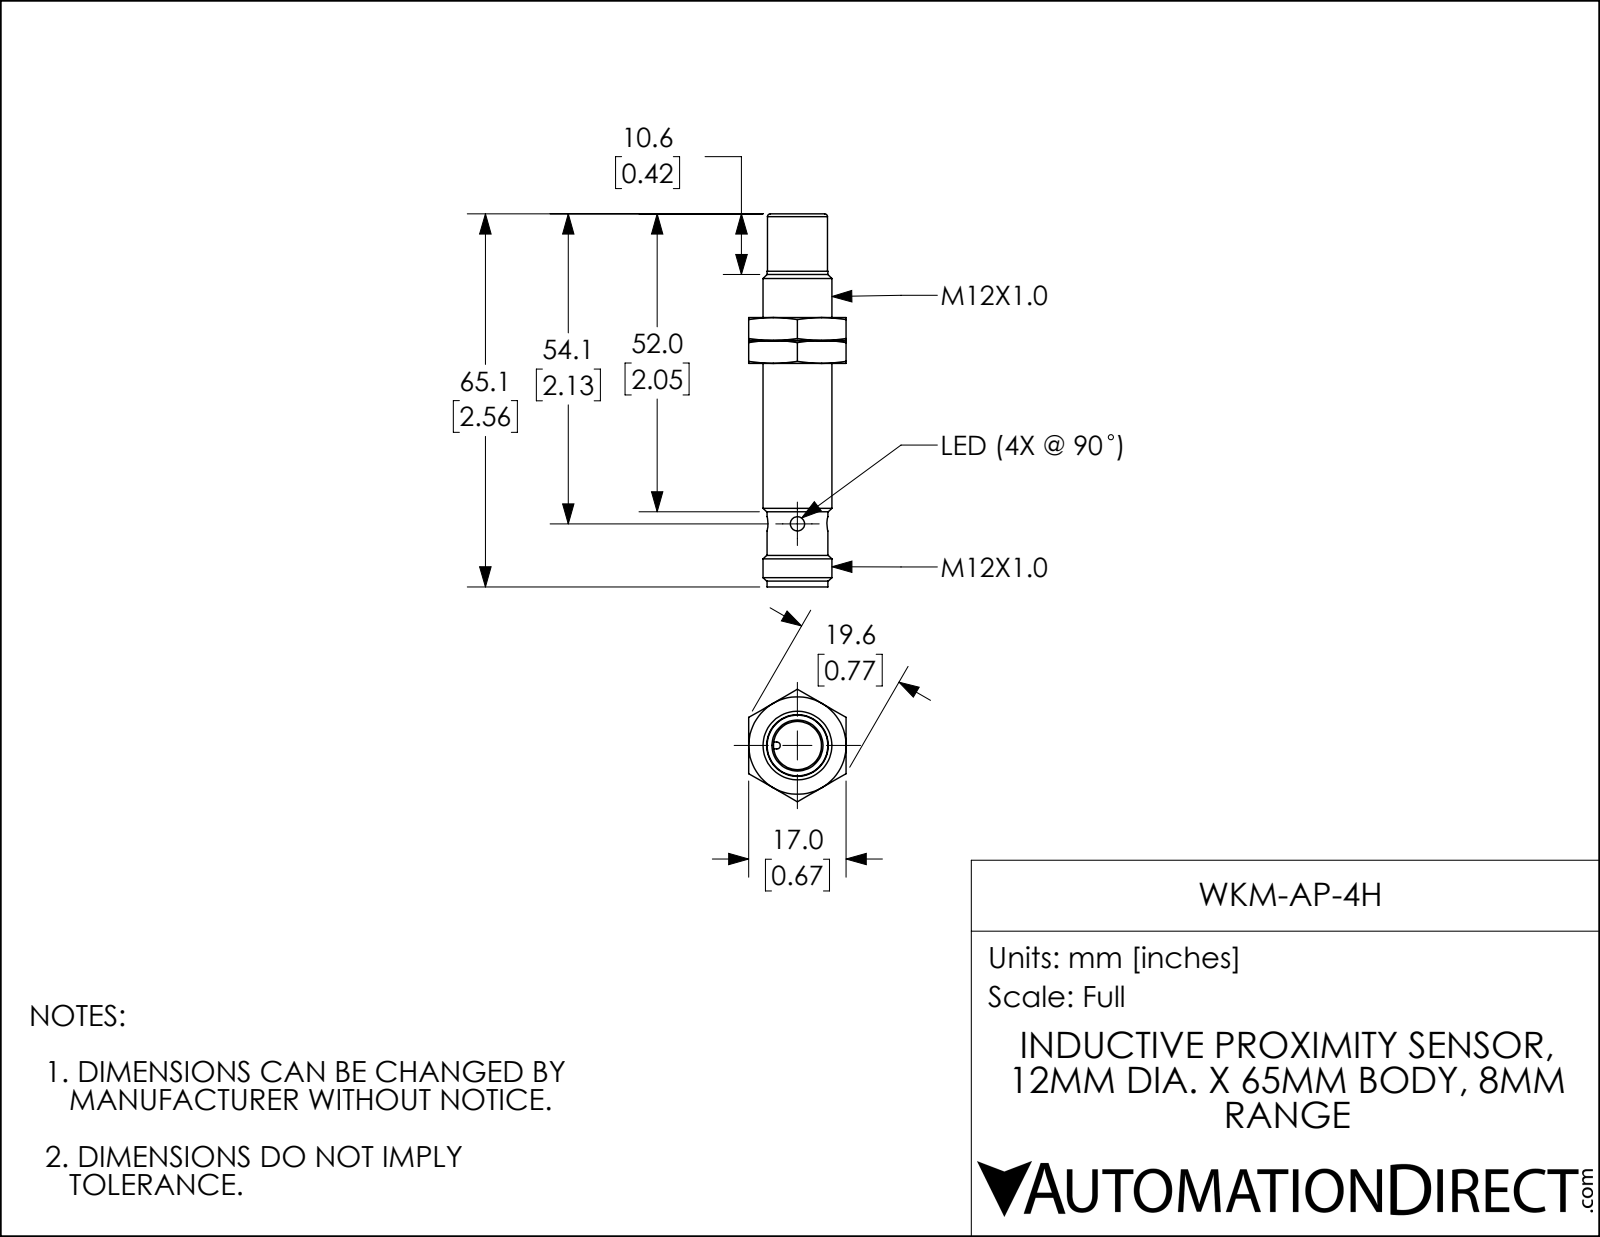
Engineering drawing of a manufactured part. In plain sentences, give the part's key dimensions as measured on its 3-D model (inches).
The part is named "WKM-AP-4H". Its 3-D file was written by "SolidWorks 2017 (AUTOMOTIVE_DESIGN)". It is 3 solids with 78 faces: 26 planar, 18 cylindrical and 34 other. Overall it measures 2.563 by 0.773 by 0.669 inches. Its volume is 0.462 cubic inches and its surface area 6.424 square inches. Round holes: 2 of diameter 0.098, 1 of diameter 0.331, 1 of diameter 0.43. Round bosses or shafts: 1 of diameter 0.472, 1 of diameter 0.417, 1 of diameter 0.413. Partial cylindrical surfaces (rounded edges, fillets, slot ends): 1 of radius 0.024, 1 of radius 0.189. The main face-to-face distances are 0.157, 0.669, 0.315, 1.028, 0.87, 0.713, 1.185, 1.343, 1.5, 2.213.
